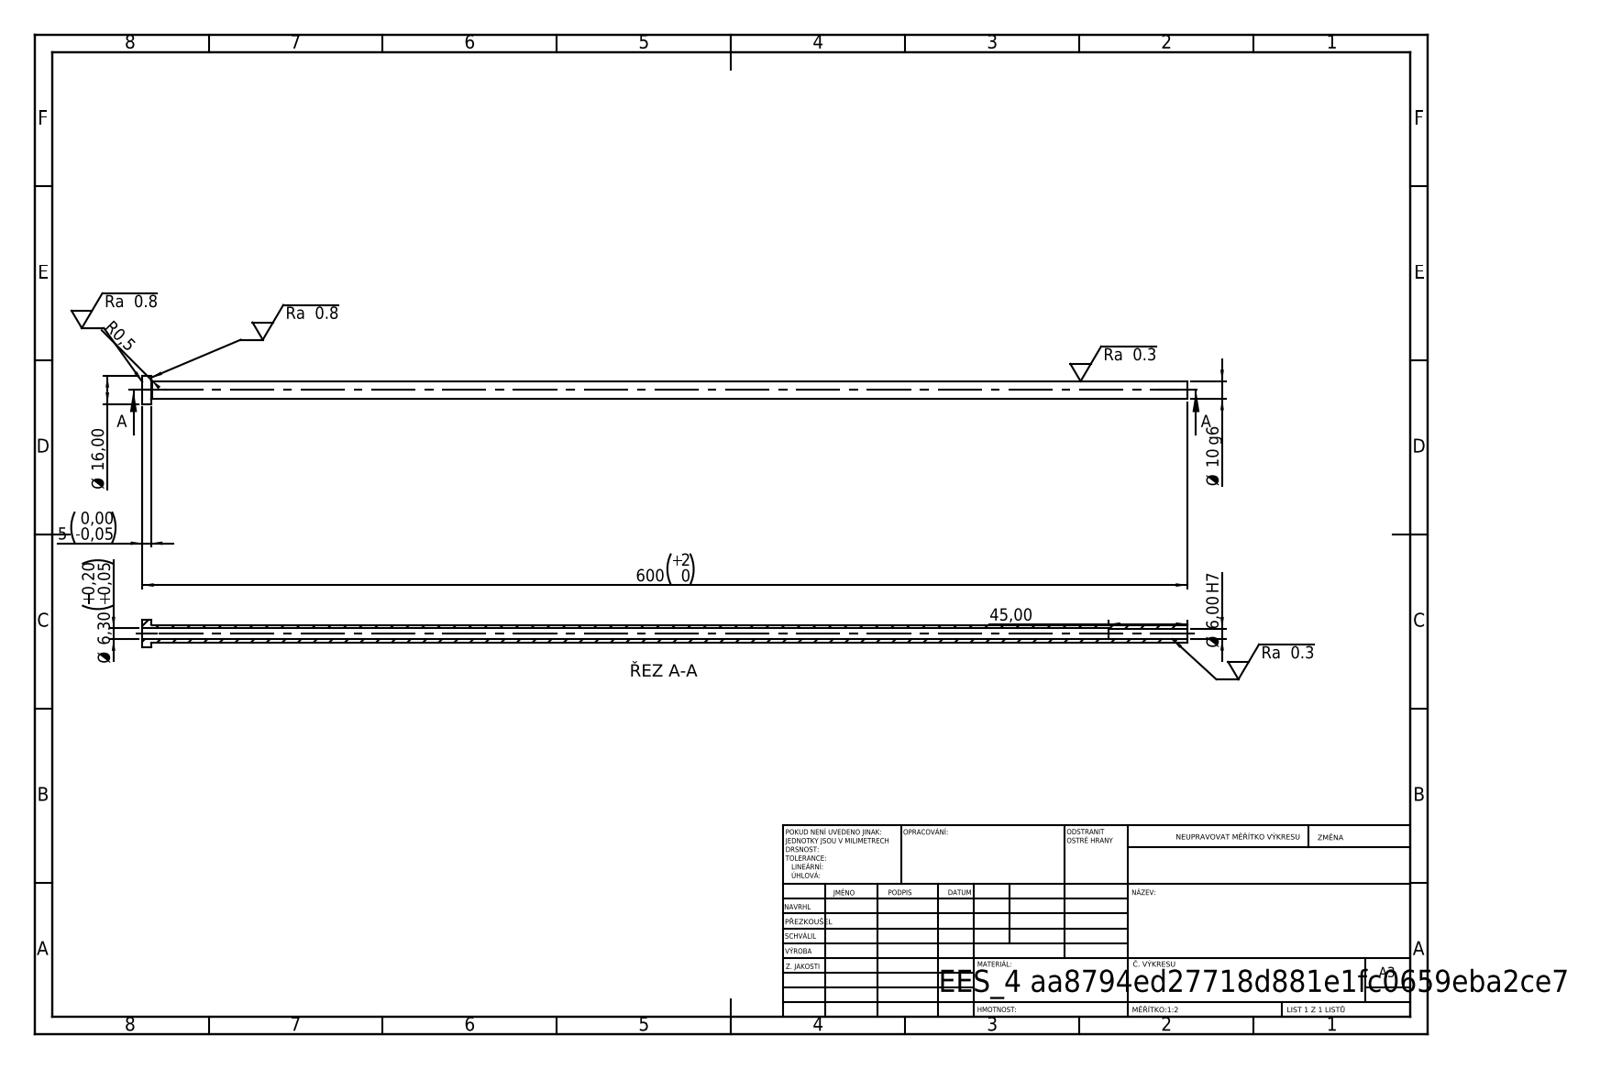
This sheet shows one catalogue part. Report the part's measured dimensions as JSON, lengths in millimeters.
{"step_written_by": "SolidWorks 2019 (CONFIG_CONTROL_DESIGN)", "units": "millimeters", "bodies": {"solids": 1, "faces": 14, "planar": 4, "cylindrical": 8, "other": 2}, "overall_size": [600, 16, 16], "volume_mm3": 29165, "surface_area_mm2": 31116, "round_holes": [[6, 1], [6.3, 1]], "round_bosses_or_shafts": [[16, 1], [10, 1]], "face_to_face_distances": [5, 600, 595, 555, 550, 45]}
